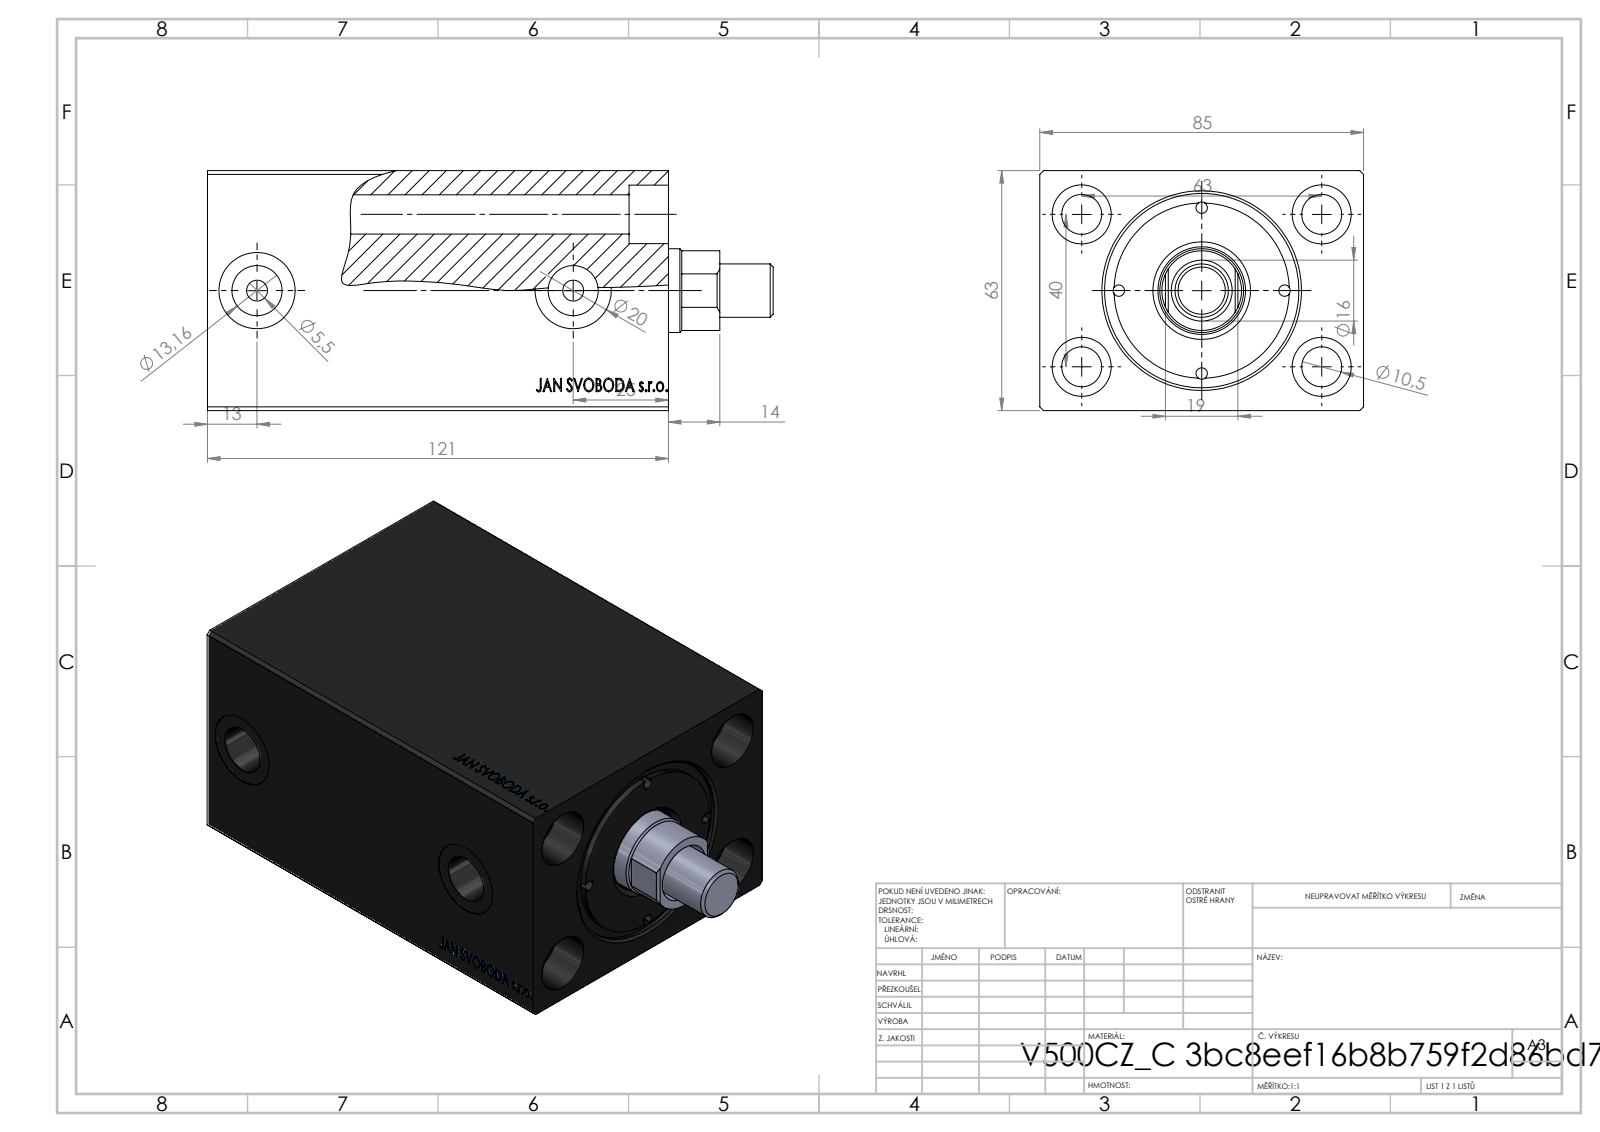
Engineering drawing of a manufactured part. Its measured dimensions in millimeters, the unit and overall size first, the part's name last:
Units: millimetres
Overall size (bounding box): 148.5 × 85 × 63
Round holes (diameter × count): ⌀3 ×4, ⌀10.5 ×4, ⌀15.5 ×4, ⌀5.5 ×2, ⌀13.16 ×2, ⌀13.6 ×2, ⌀20 ×2, ⌀16 ×1, ⌀22 ×1, ⌀23 ×1, ⌀36 ×1, ⌀40 ×1
Round bosses / shafts (diameter × count): ⌀46 ×1, ⌀14 ×1, ⌀12 ×1
Partial cylindrical surfaces — rounded edges, fillets, slot ends (radius × count): R10.46 ×1
Main face-to-face distances: 63, 85, 121, 36, 11.8, 73.2, 109.2, 10, 1.8, 120.8
Hole centre spacings: 21.75, 22.25, 30.76, 31.55, 37.31, 52.3, 56.88, 40
Volume: 550 370 mm³ · Surface area: 95 719 mm²
Bodies: 4 solids, 904 faces (417 planar, 85 cylindrical, 402 other)
Part name (STEP PRODUCT): V500CZ_C; V500CZ_VC_vysunovaci_C; V500CZ_VCP_C; V500CZ_FM
STEP written by: SolidWorks 2019 (CONFIG_CONTROL_DESIGN)
